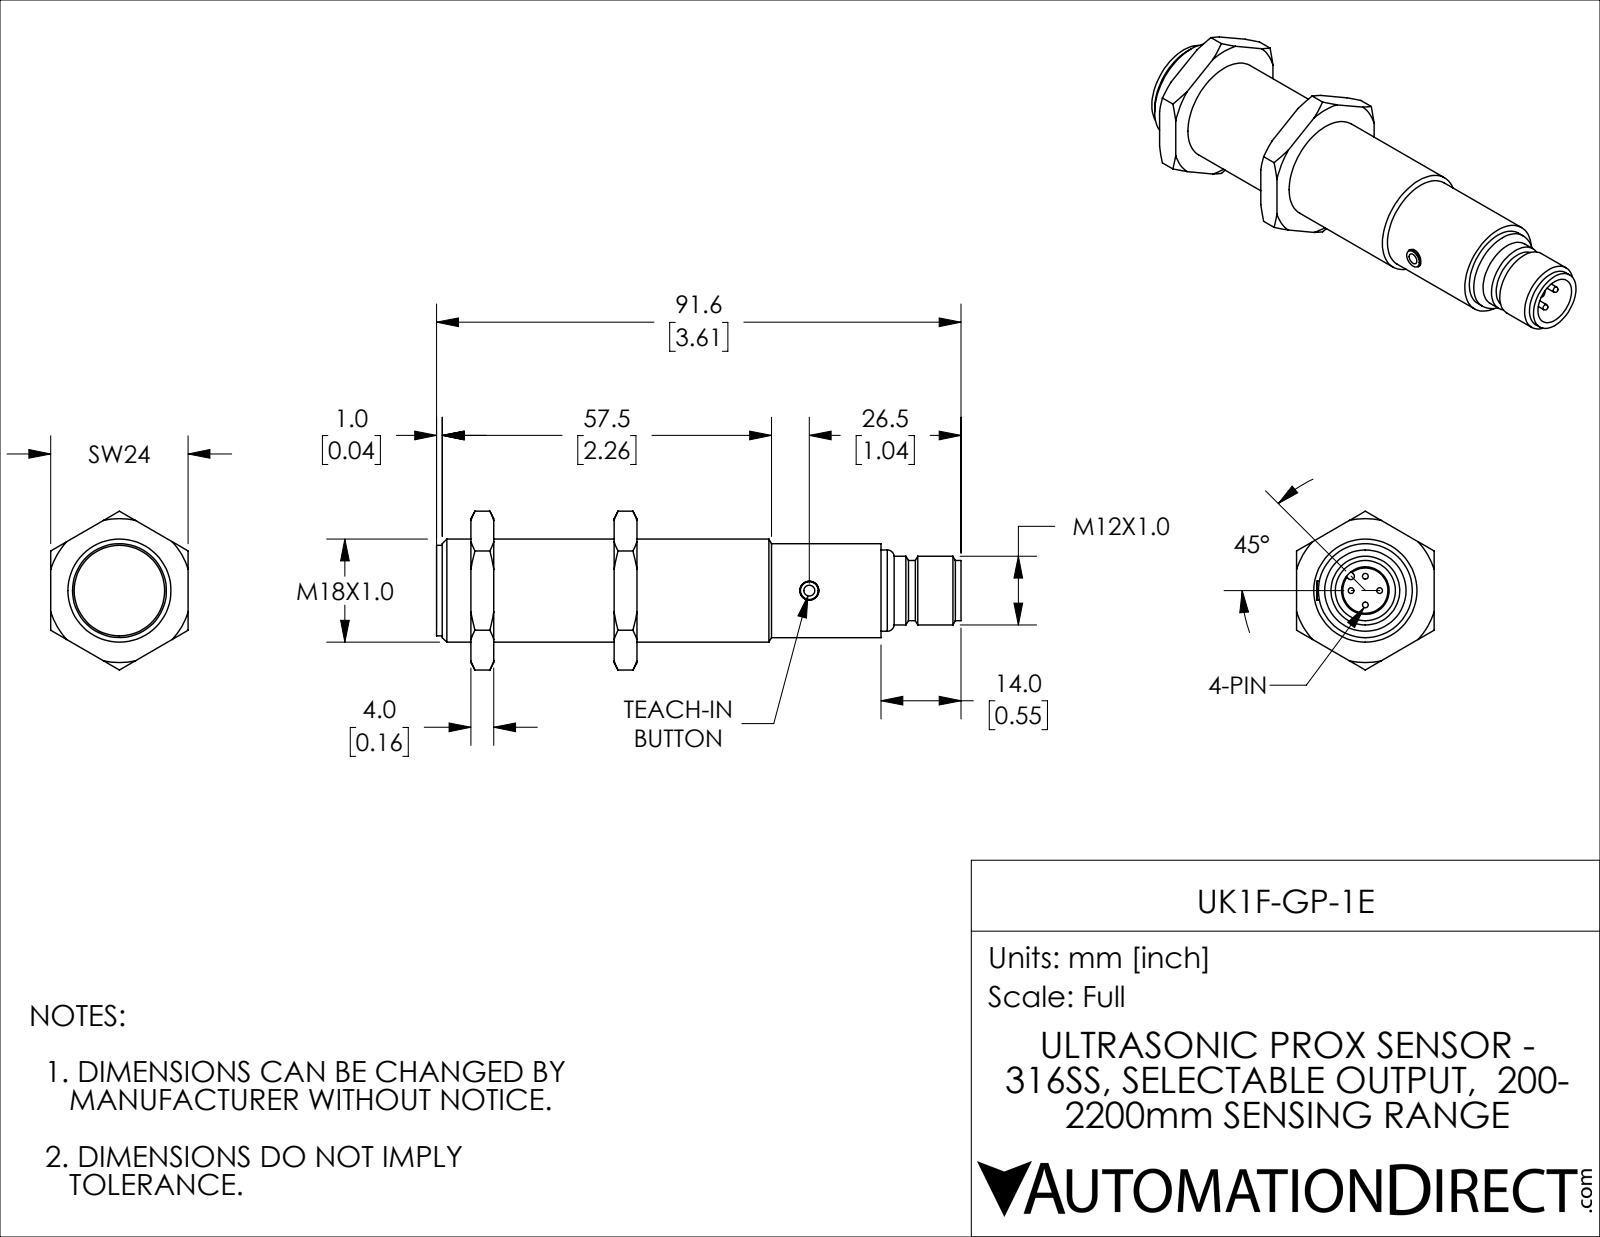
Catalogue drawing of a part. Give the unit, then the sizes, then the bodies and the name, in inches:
Units: inches
Overall size (bounding box): 3.606 × 1.091 × 0.945
Round holes (diameter × count): ⌀0.13 ×1, ⌀0.327 ×1, ⌀0.709 ×1
Round bosses / shafts (diameter × count): ⌀0.039 ×4, ⌀0.646 ×1, ⌀0.622 ×1, ⌀0.559 ×1, ⌀0.472 ×1, ⌀0.413 ×1
Partial cylindrical surfaces — rounded edges, fillets, slot ends (radius × count): R0.024 ×1
Main face-to-face distances: 0.984, 0.157, 0.945, 1.142, 0.827, 0.236, 0.394, 1.22, 1.378, 3.055
Volume: 1.338 in³ · Surface area: 11.97 in²
Bodies: 4 solids, 113 faces (27 planar, 35 cylindrical, 51 other)
Part name (STEP PRODUCT): UK1F-GP-1E
STEP written by: SolidWorks 2018 (AUTOMOTIVE_DESIGN)
